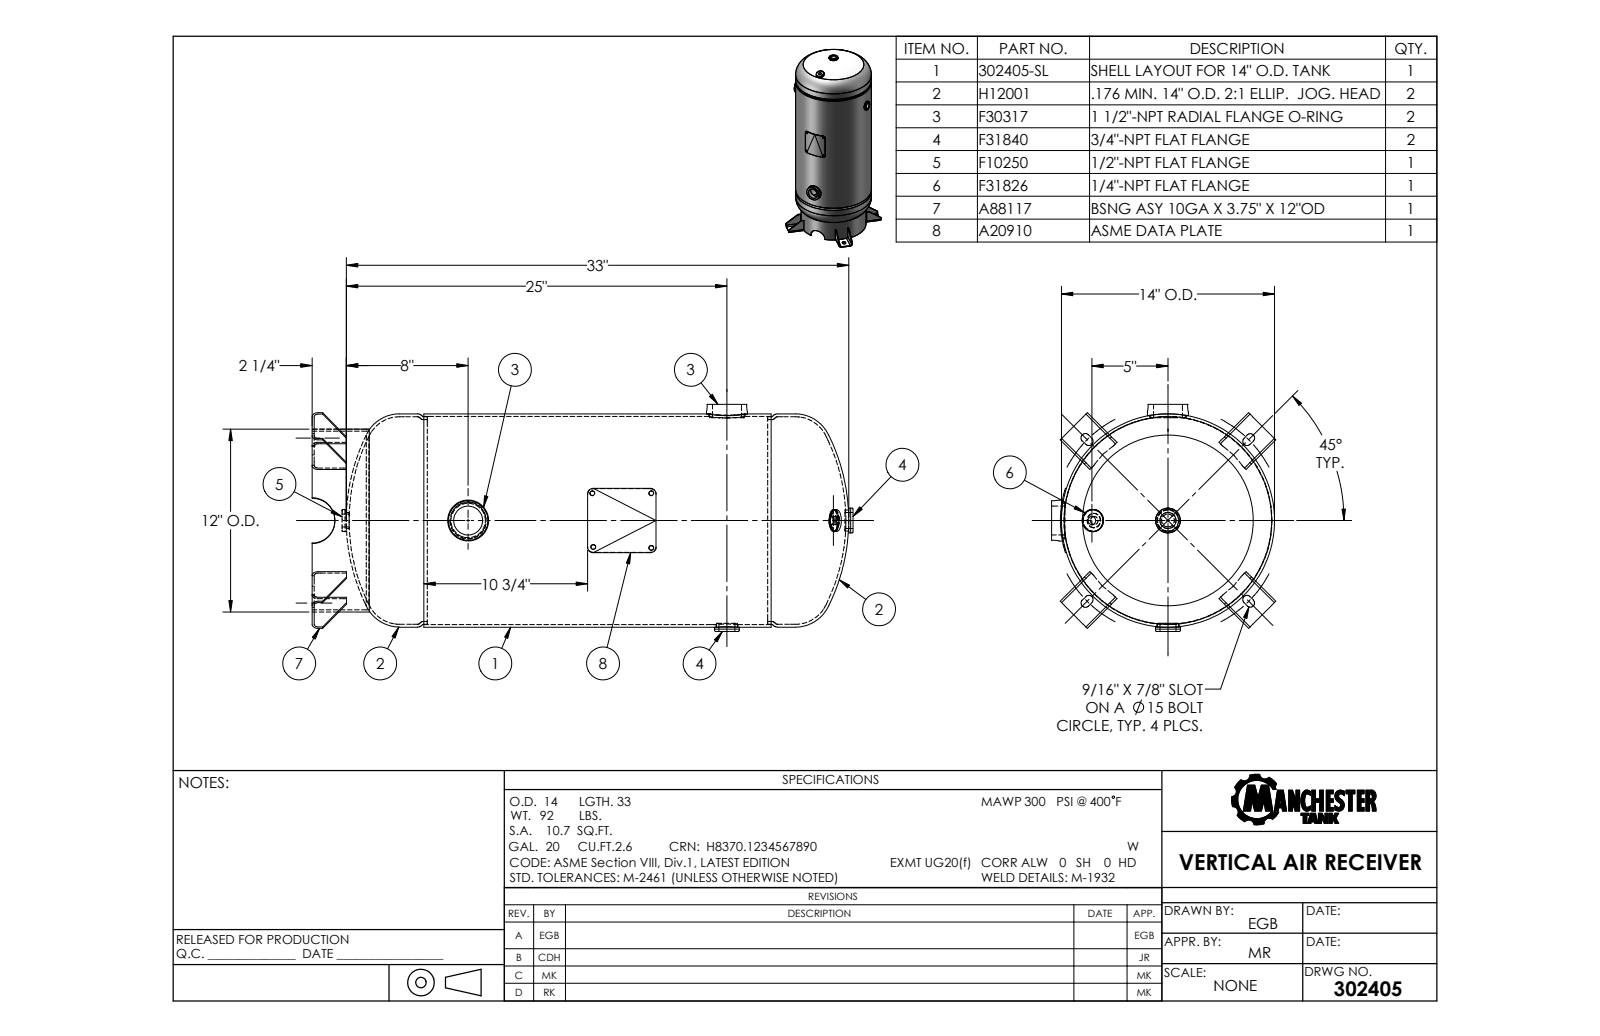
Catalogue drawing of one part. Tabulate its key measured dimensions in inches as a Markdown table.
| quantity | value |
| --- | --- |
| part name | 302405 |
| STEP written by | SolidWorks 2020 (AUTOMOTIVE_DESIGN) |
| units | inches |
| bodies | 15 solids, 343 faces (126 planar, 101 cylindrical, 116 other) |
| overall size | 35.895 × 15.25 × 14.68 |
| volume | 308.3 in³ |
| surface area | 3 655 in² |
| round holes (diameter × count) | 1.05 × 2, 1.9 × 2, 0.54 × 1, 0.84 × 1, 1.065 × 1, 1.253 × 1, 1.503 × 1, 11.732 × 1, 13.25 × 1, 13.625 × 1, 13.658 × 1 |
| round bosses / shafts (diameter × count) | 2.688 × 2, 2.266 × 2, 14 × 1, 13.62 × 1, 12 × 1, 2.063 × 1, 2.062 × 1, 1.813 × 1 |
| partial cylindrical surfaces (radius × count) | 0.25 × 8, 0.281 × 8, 0.384 × 8, 7.5 × 2, 7.06 × 1 |
| main face-to-face distances | 0.134, 2.383, 0.196, 22.554, 2.517, 2.25, 22.357, 29.846, 29.98, 7.489 |
